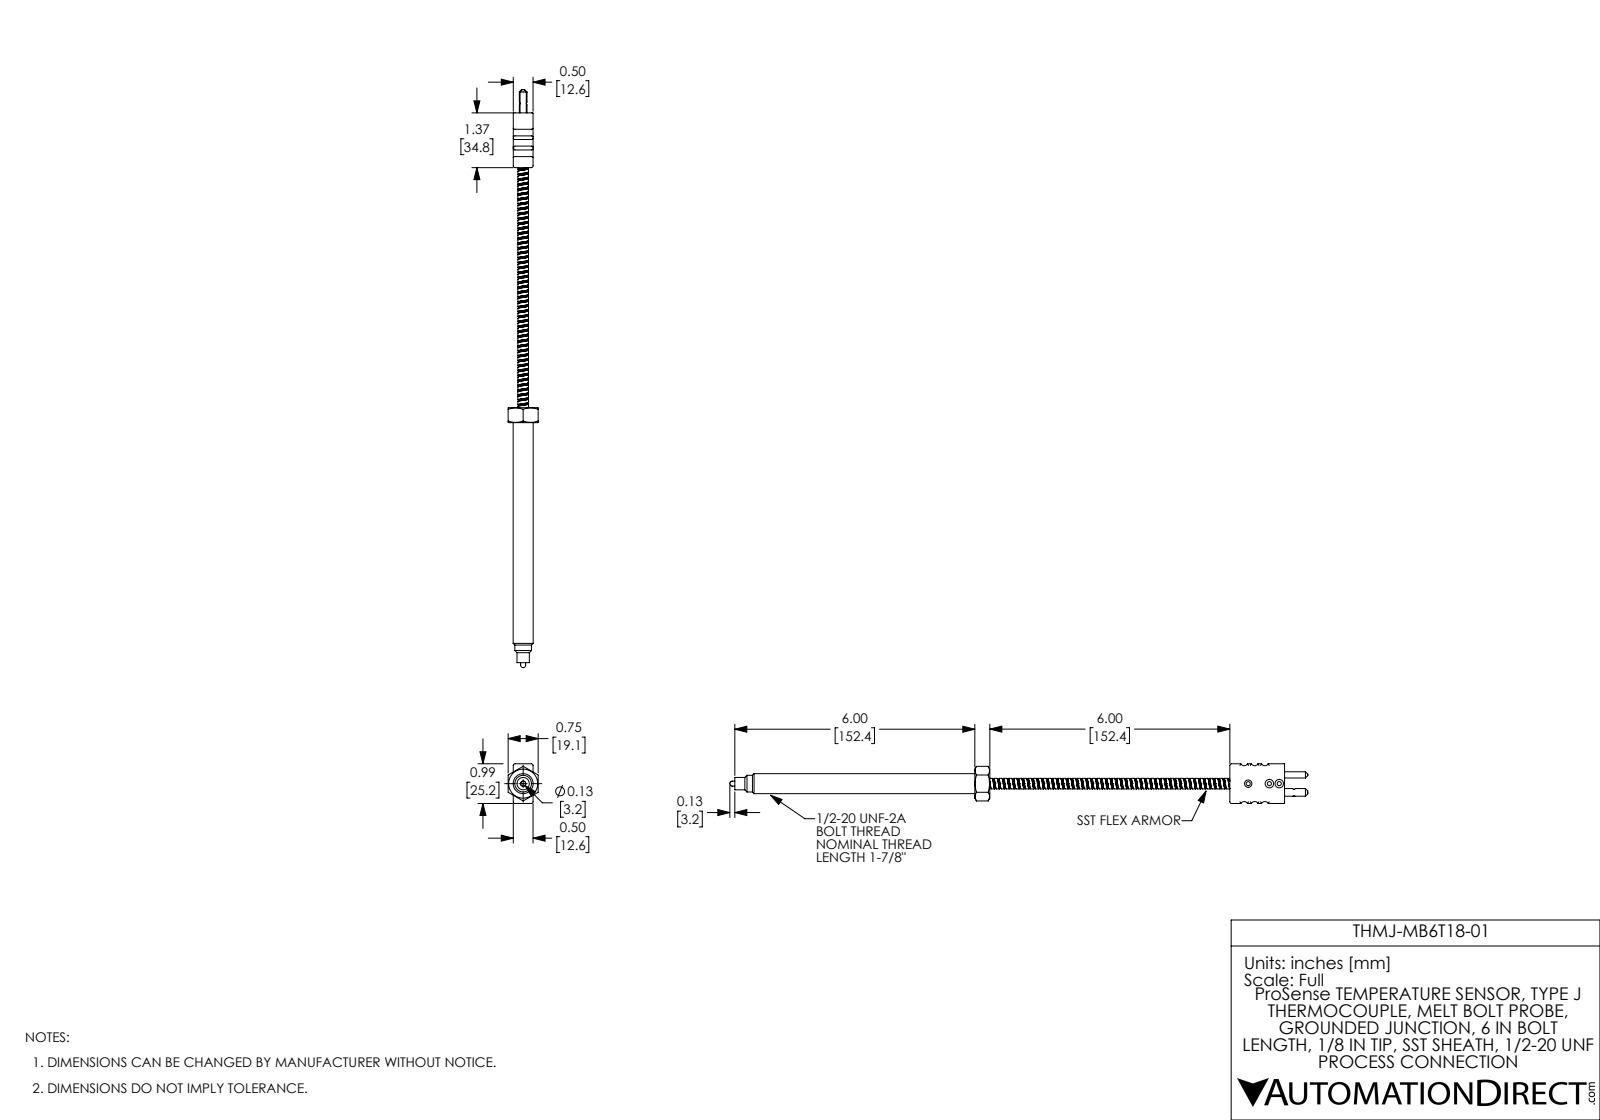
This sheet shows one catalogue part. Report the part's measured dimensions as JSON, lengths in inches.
{"part_name": "THMJ-MB6T18-01", "step_written_by": "SolidWorks 2017 (AUTOMOTIVE_DESIGN)", "units": "inches", "bodies": {"solids": 3, "faces": 312, "planar": 69, "cylindrical": 172, "other": 71}, "overall_size": [14.451, 0.993, 0.75], "volume_in3": 2.273, "surface_area_in2": 23.87, "round_holes": [[0.103, 2], [0.158, 2], [0.135, 1], [0.185, 1], [0.294, 1], [0.308, 1]], "round_bosses_or_shafts": [[0.5, 1], [0.417, 1], [0.309, 1], [0.278, 1], [0.265, 1], [0.191, 1], [0.156, 1], [0.125, 1]], "partial_cylinders_radius": [[0.045, 8], [0.095, 6], [0.01, 4]], "face_to_face_distances": [0.495, 0.75, 7.369, 6, 0.993, 0.127, 0.622, 1.369, 6.375, 7.744], "hole_center_spacings": [0.217, 0.328, 0.572, 0.247, 0.433, 0.529, 0.776]}
